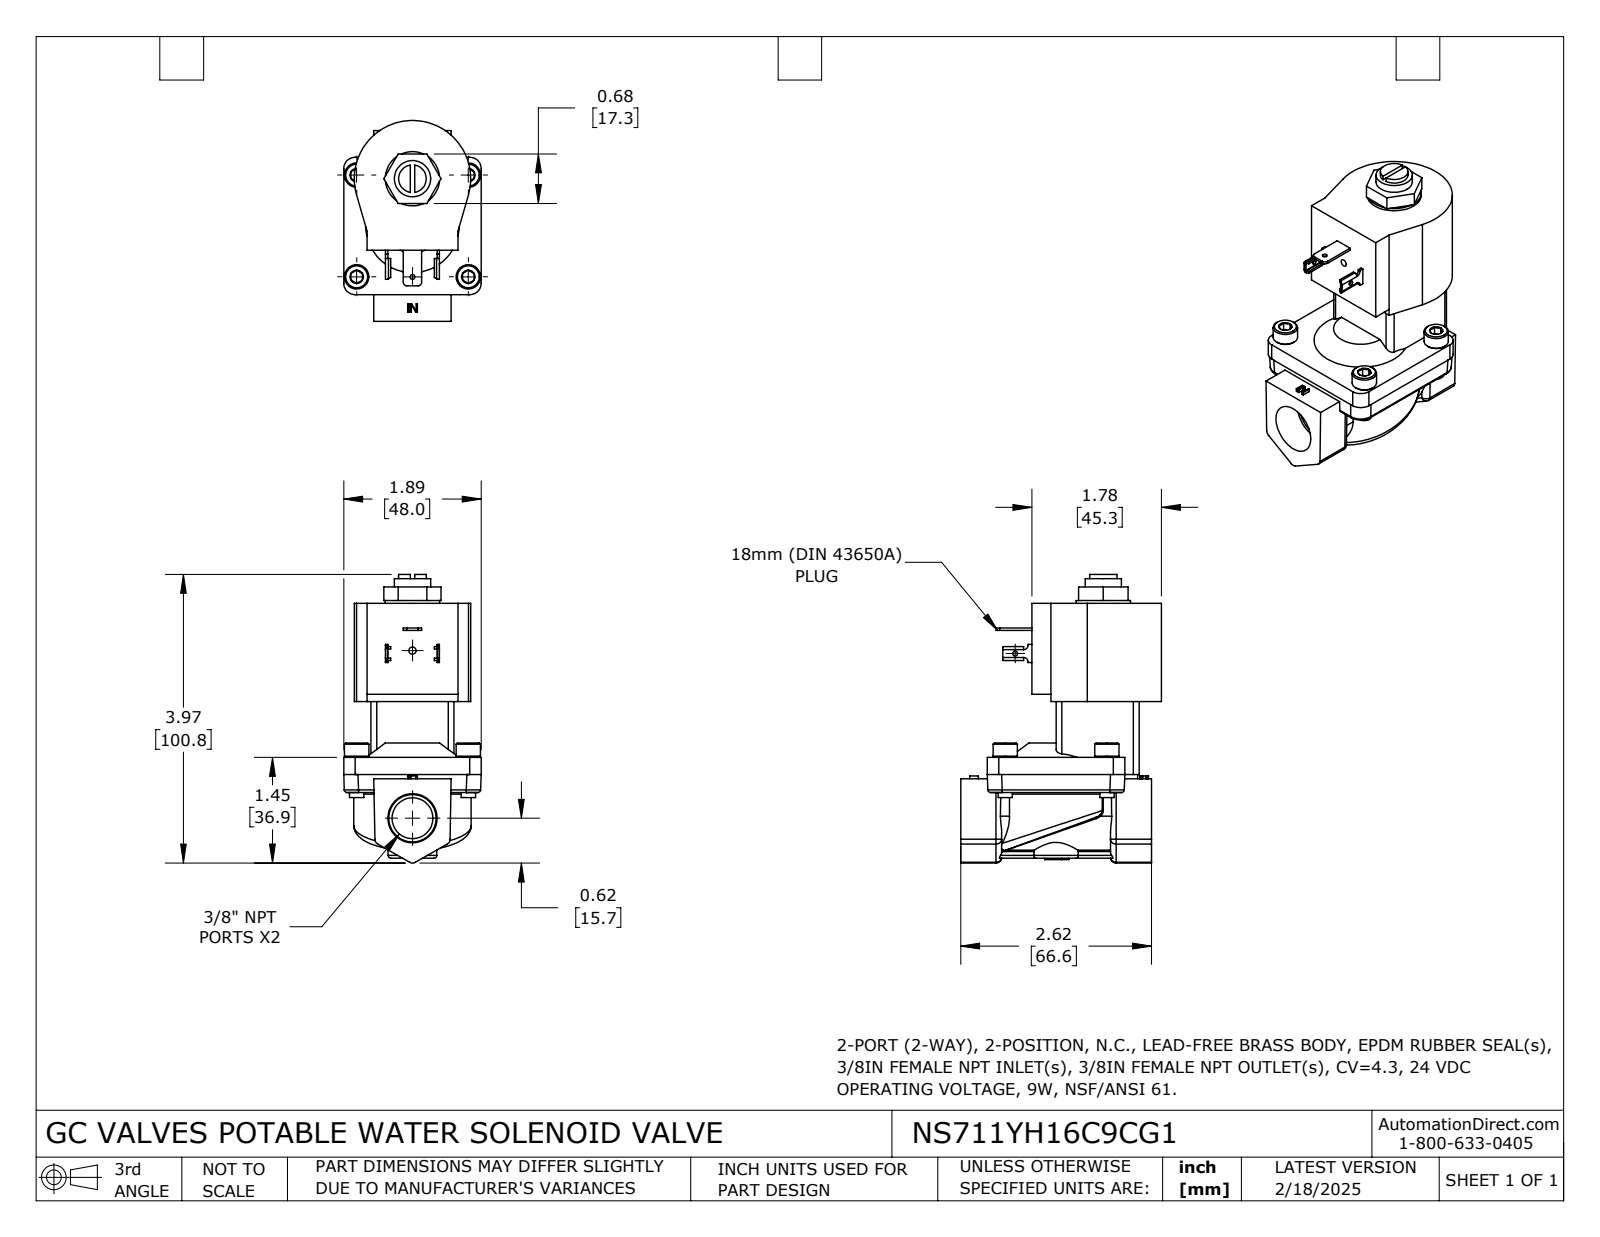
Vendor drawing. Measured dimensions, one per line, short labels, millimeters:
name: NS711YH16C9CG1
written by: SolidWorks 2024 (CONFIG_CONTROL_DESIGN)
unit: mm
bodies: 1 solid, 486 faces (270 planar, 113 cylindrical, 103 other)
size: 100.77 × 70.12 × 48
volume: 134 803 mm³; area: 25 680 mm²
holes: 1× ⌀1.68, 1× ⌀1.7, 1× ⌀2.53, 1× ⌀14.27, 1× ⌀30.48
bosses: 4× ⌀8.5, 4× ⌀5, 1× ⌀18.95, 1× ⌀12.67, 1× ⌀9.65
rounds: 15× R2, 6× R0.5, 6× R1, 4× R0.15, 4× R1.04, 4× R4, 4× R5, 2× R1.27
face distances: 19.5, 34.29, 53.79, 29, 22.04, 2.54, 31.75, 33.3, 37.44, 9.5
hole spacings: 34.29, 58.5
